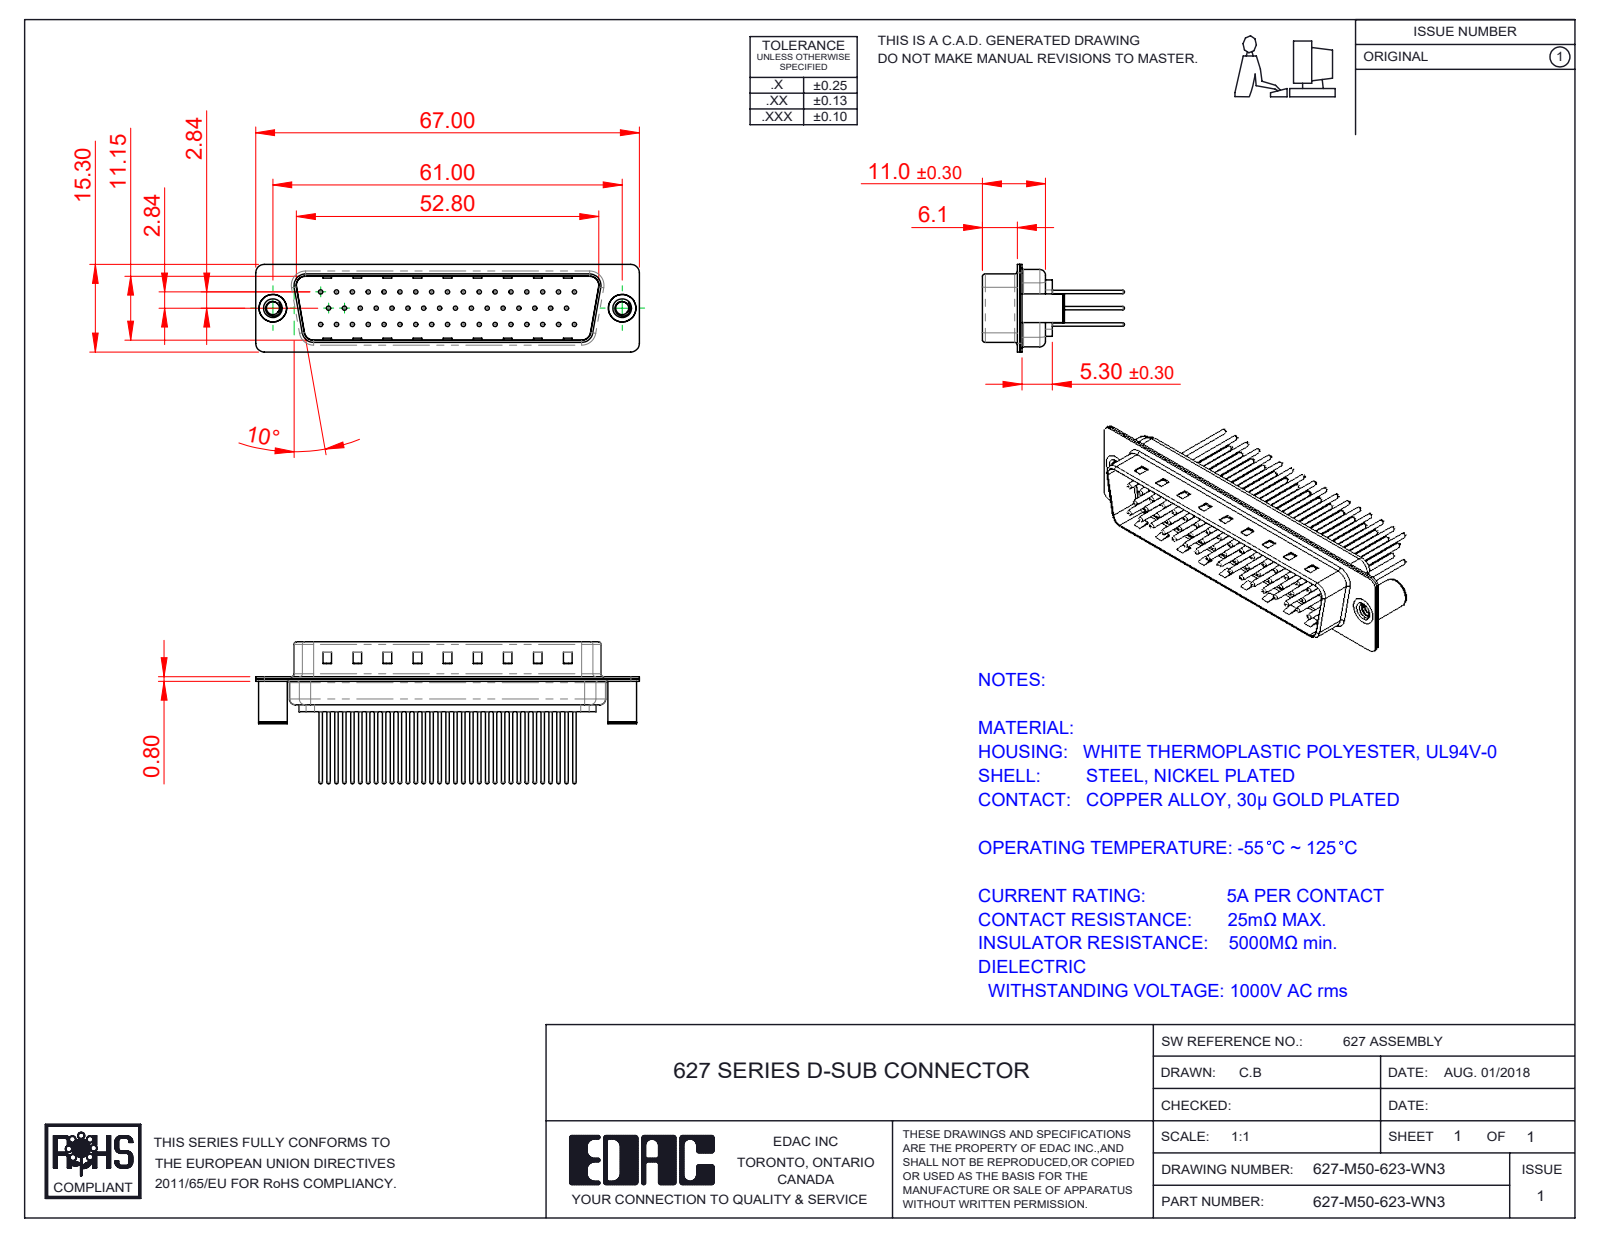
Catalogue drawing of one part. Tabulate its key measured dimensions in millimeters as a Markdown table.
| quantity | value |
| --- | --- |
| part name | 627M 4-40 Threaded Board Spacer; 627M Contact Row 1_23; 627M Shell Front_50 Contacts; 627M Contact Row 3_23 (+4 more) |
| STEP written by | SolidWorks 2020 (CONFIG_CONTROL_DESIGN) |
| units | millimeters |
| bodies | 55 solids, 2296 faces (553 planar, 865 cylindrical, 878 other) |
| overall size | 67 × 24.77 × 15.3 |
| volume | 4 745 mm³ |
| surface area | 11 605 mm² |
| round holes (diameter × count) | 0.75 × 50, 1.6 × 50, 2 × 50, 2.26 × 2, 3.26 × 2, 4 × 2, 4.8 × 2 |
| round bosses / shafts (diameter × count) | 1.5 × 50, 0.6 × 50, 5 × 2, 4.9 × 2 |
| partial cylindrical surfaces (radius × count) | 1.5 × 16, 2 × 12, 0.5 × 8, 1.6 × 8, 0.25 × 4, 0.6 × 4, 0.65 × 4, 0.9 × 4 |
| main face-to-face distances | 0.4, 11.55, 5.7, 6.1, 0.78, 0.77, 12.33, 5.3, 12.32, 13.1 |
| hole center spacings | 3.16, 2.77, 5.54, 8.31, 11.08, 13.85, 16.62, 5.03 |
